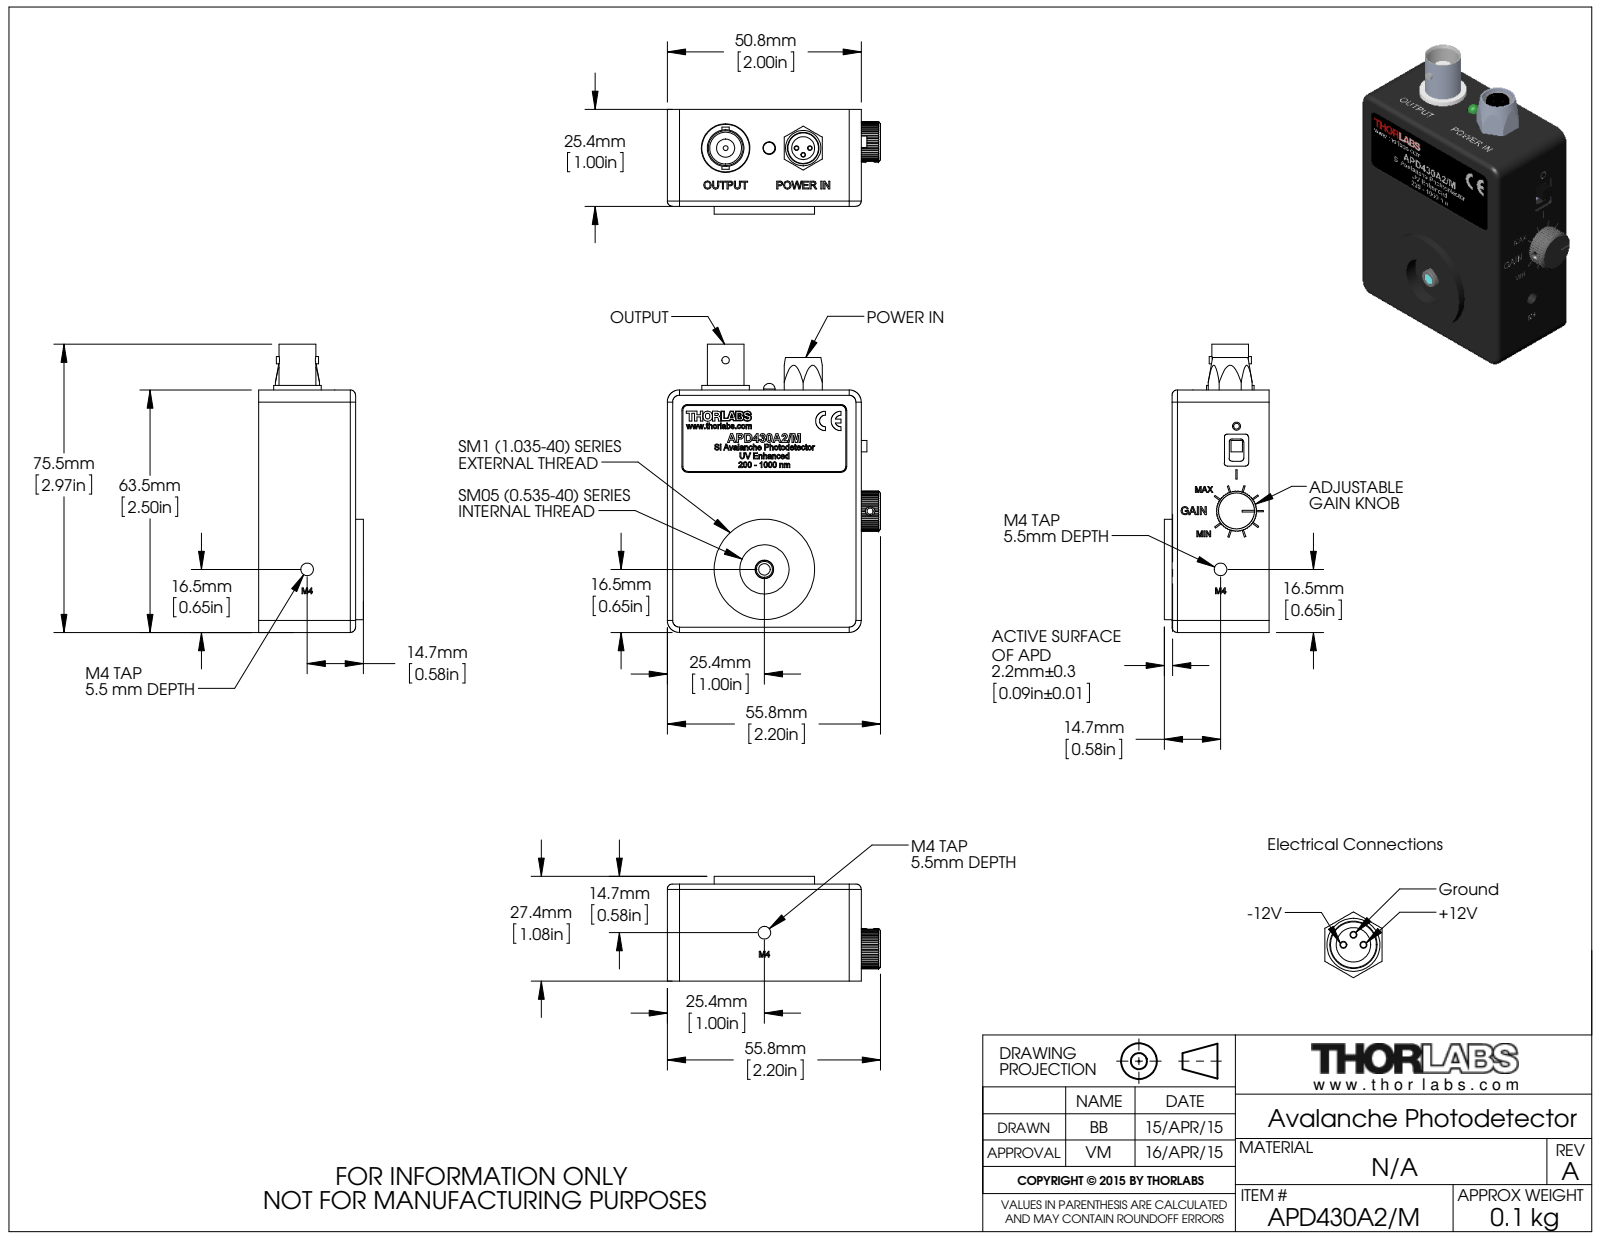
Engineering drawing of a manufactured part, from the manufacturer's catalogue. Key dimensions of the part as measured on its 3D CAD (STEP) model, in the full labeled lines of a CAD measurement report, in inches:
Part name (STEP PRODUCT): MTN004940
STEP written by: SolidWorks 2014 (AUTOMOTIVE_DESIGN)
Units: inches
Bodies: 0 solids, 2474 faces (1336 planar, 436 cylindrical, 702 other)
Overall size (bounding box): 2.971 × 2.197 × 1.08
Round holes (diameter × count): ⌀0.063 ×9, ⌀0.02 ×6, ⌀0.094 ×4, ⌀0.018 ×2, ⌀0.098 ×2, ⌀0.13 ×2, ⌀0.05 ×1, ⌀0.052 ×1, ⌀0.083 ×1, ⌀0.118 ×1, ⌀0.13 ×1, ⌀0.138 ×1
Round bosses / shafts (diameter × count): ⌀0.039 ×5, ⌀0.15 ×4, ⌀0.079 ×4, ⌀0.065 ×2, ⌀0.063 ×2, ⌀0.051 ×2, ⌀1.035 ×1, ⌀0.49 ×1
Partial cylindrical surfaces — rounded edges, fillets, slot ends (radius × count): R0.012 ×53, R0.125 ×19, R0.13 ×14, R0.031 ×8, R0.095 ×8, R0.02 ×6, R0.075 ×6, R0.008 ×5
Main face-to-face distances: 0.063, 0.1, 0.016, 0.935, 0.872, 0.065, 1, 0.937, 0.984, 0.922
Hole centre spacings: 1.621, 0.174, 2.013, 2.579, 0.098, 1.711, 0.05, 0.079
